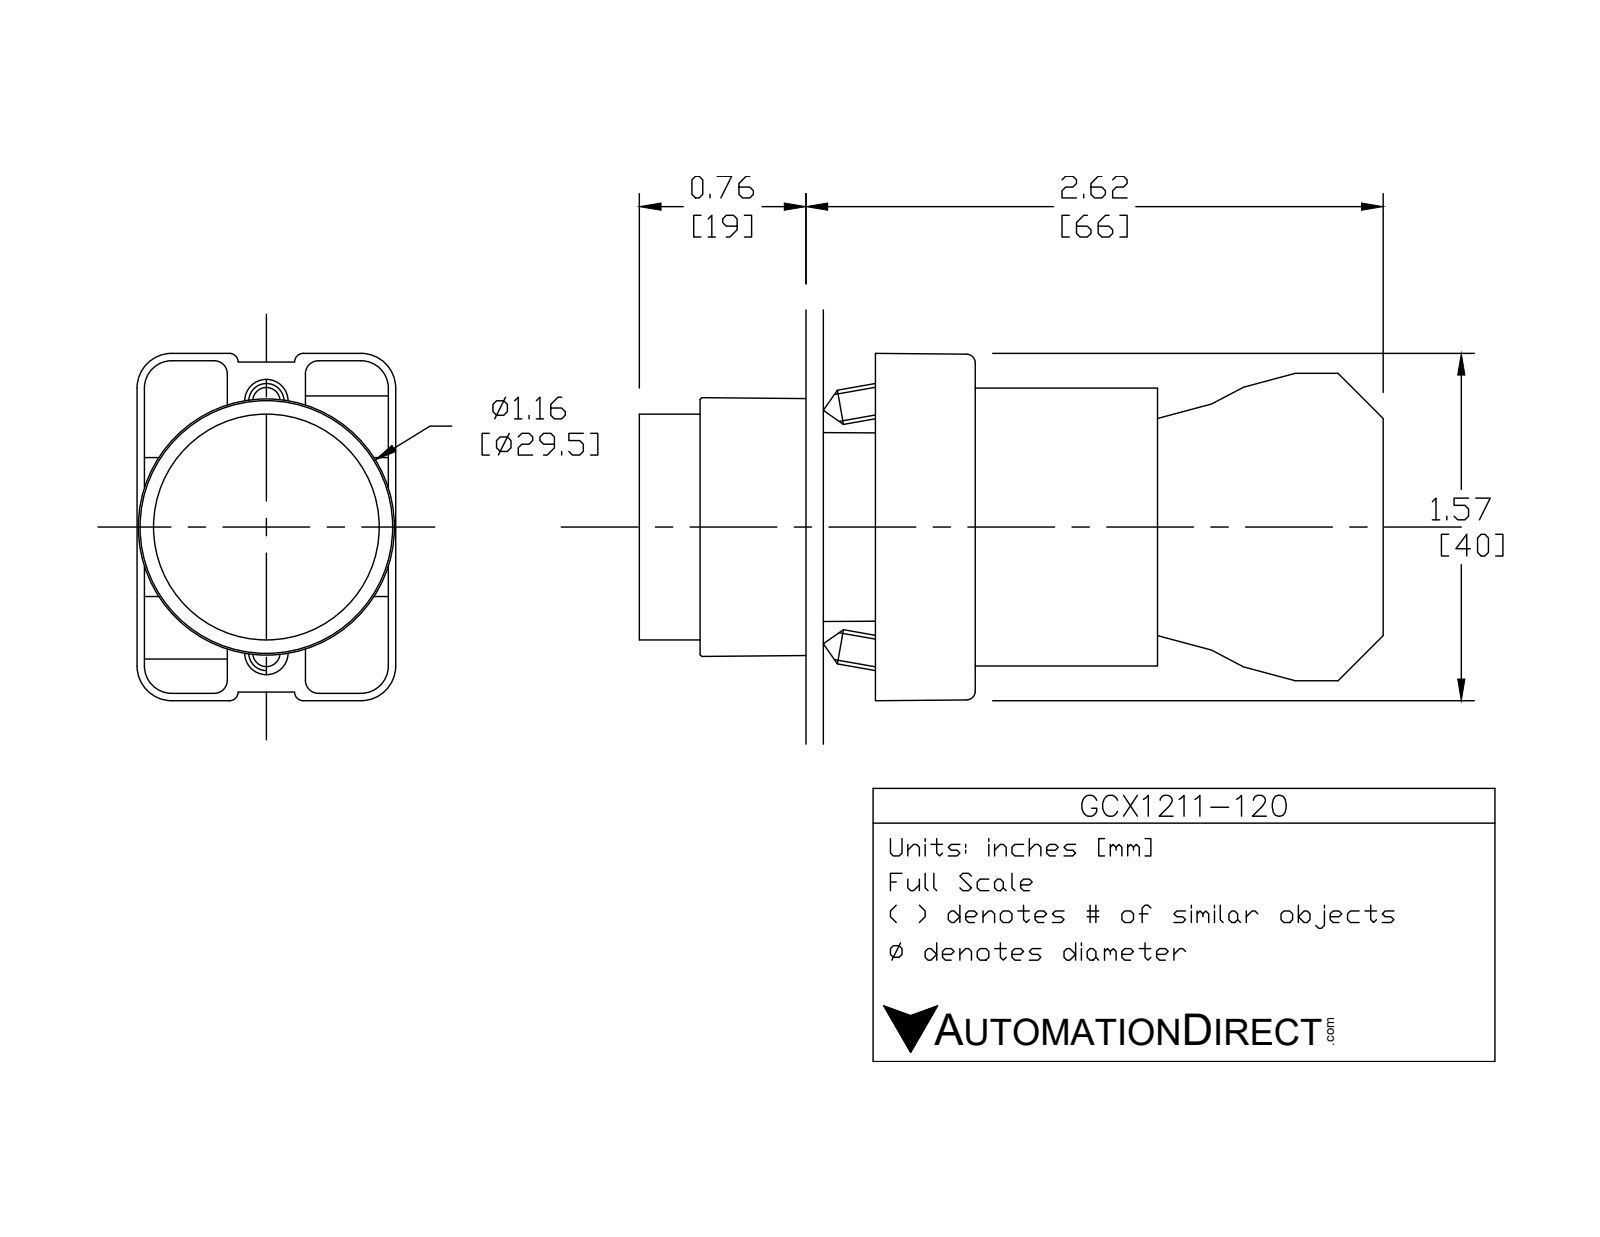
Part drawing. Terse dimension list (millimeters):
name: ECX1050; GCX1211-120; ecx1030; GCX1211 OPERATOR (+1 more)
written by: SolidWorks 2016 (AUTOMOTIVE_DESIGN)
unit: mm
bodies: 7 solids, 425 faces (250 planar, 144 cylindrical, 31 other)
size: 84.3 × 40.2 × 29.9
volume: 44 590 mm³; area: 23 430 mm²
holes: 2× ⌀2, 2× ⌀3.1, 2× ⌀3.3, 1× ⌀2.2, 1× ⌀5, 1× ⌀11.9, 1× ⌀22.3, 1× ⌀22.6, 1× ⌀26
bosses: 4× ⌀4, 1× ⌀29.8, 1× ⌀25.5, 1× ⌀24, 1× ⌀21.7, 1× ⌀19.8, 1× ⌀12.8
rounds: 24× R1.5, 12× R1, 12× R3.1, 12× R4, 8× R1, 2× R3.3, 1× R0.5, 1× R1.6
face distances: 21, 14.7, 29.7, 51.3, 30.3, 0.8, 0.8, 14.6, 29.6, 15.1
hole spacings: 6, 13.8, 12, 12.4
